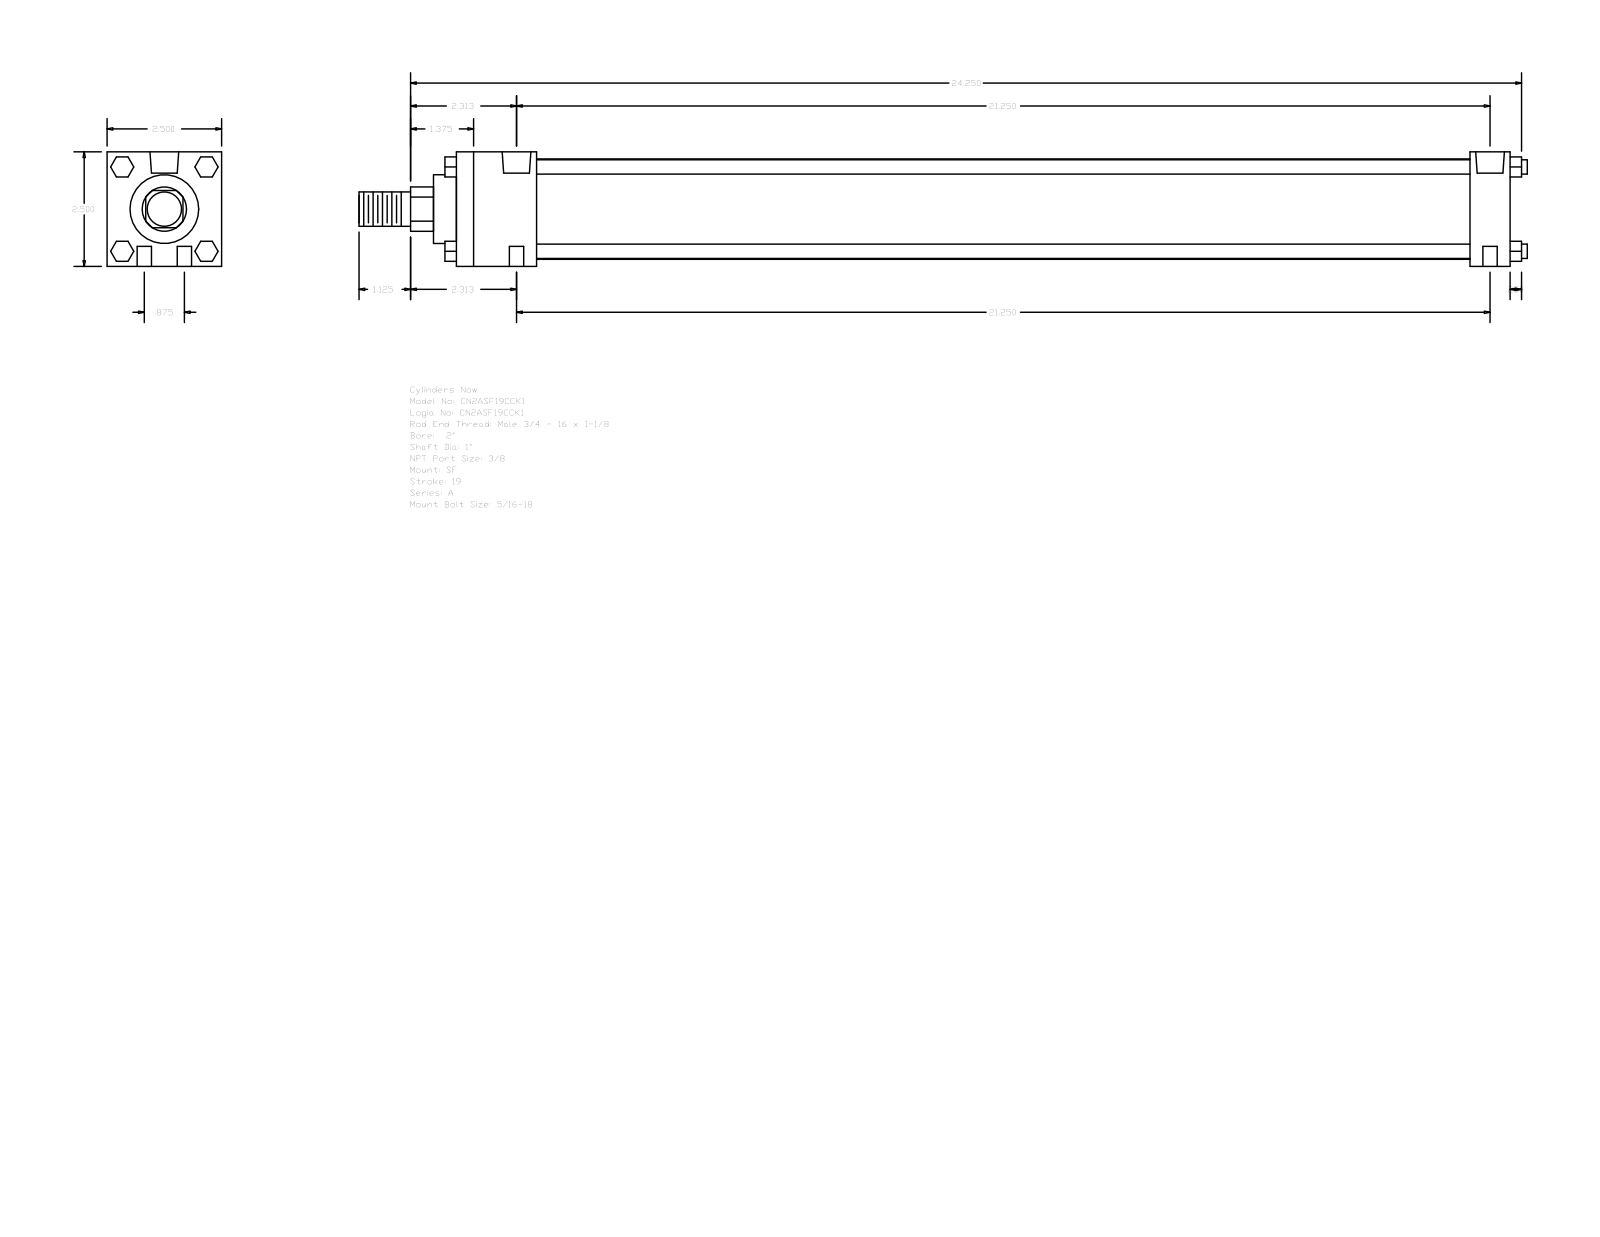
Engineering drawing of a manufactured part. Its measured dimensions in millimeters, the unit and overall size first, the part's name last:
Units: millimetres
Overall size (bounding box): 647.7 × 63.5 × 63.5
Round holes (diameter × count): ⌀7.94 ×4, ⌀5.56 ×2, ⌀15.93 ×2
Round bosses / shafts (diameter × count): ⌀7.94 ×4, ⌀55.63 ×1, ⌀38.1 ×1, ⌀25.4 ×1, ⌀19.05 ×1
Partial cylindrical surfaces — rounded edges, fillets, slot ends (radius × count): R12.29 ×1
Main face-to-face distances: 63.5, 584.2, 561.98, 22.22, 44.45, 517.53, 539.75, 12.7, 596.9, 6.35
Hole centre spacings: 11.11, 539.86, 539.75, 22.22, 540.21, 534.18
Bodies: 0 solids, 124 faces (94 planar, 30 cylindrical, 0 other)
Part name (STEP PRODUCT): A_SF__0200_1
STEP written by: GSSL Pune (CONFIG_CONTROL_DESIGN)
